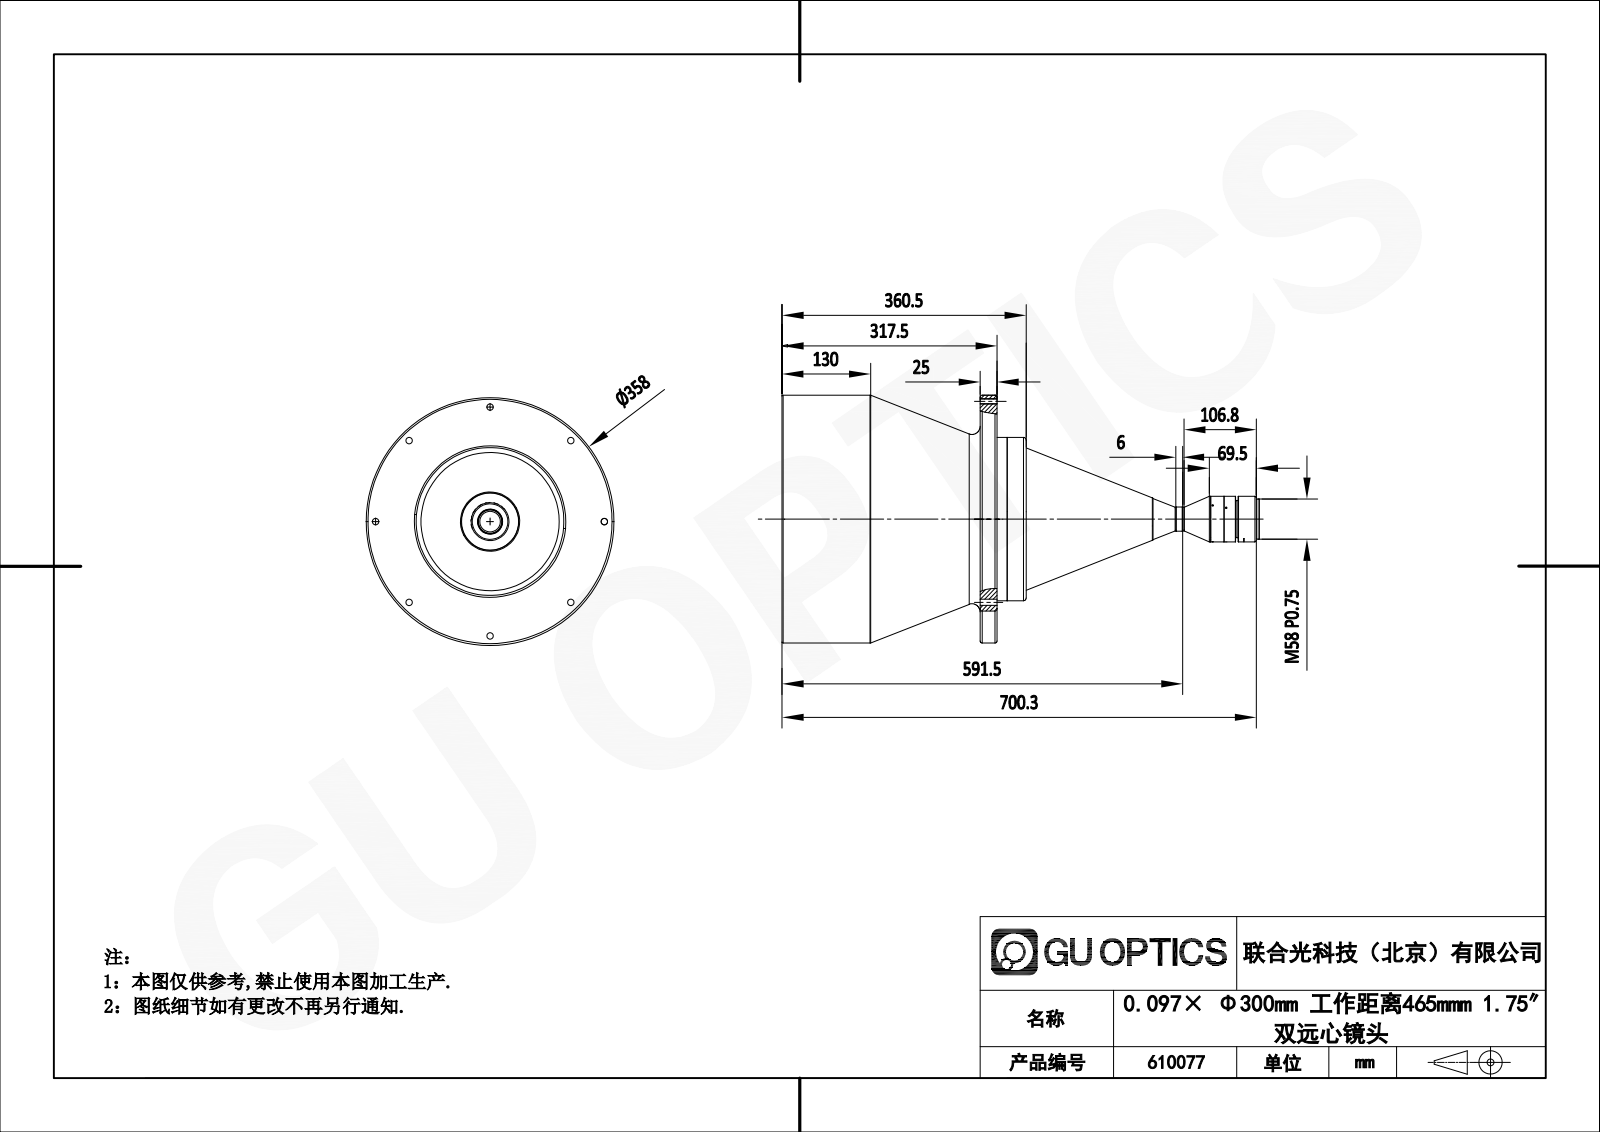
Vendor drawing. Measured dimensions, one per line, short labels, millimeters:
name: DTCM175-300S-M58-AL
written by: SolidWorks 2017 (CONFIG_CONTROL_DESIGN)
unit: mm
bodies: 1 solid, 159 faces (26 planar, 71 cylindrical, 62 other)
size: 704.76 × 358 × 358
volume: 31 790 000 mm³; area: 709 218 mm²
holes: 6× ⌀2.4, 4× ⌀6.8, 4× ⌀9, 1× ⌀32, 1× ⌀206, 1× ⌀340
bosses: 1× ⌀358, 1× ⌀236, 1× ⌀66, 1× ⌀58, 1× ⌀56.8, 1× ⌀35, 1× ⌀34, 1× ⌀31
rounds: 1× R1.25, 1× R1.75, 1× R3
face distances: 25, 68, 43, 292.5, 317.5, 360.5, 704.76, 412.26, 387.26, 344.26
hole spacings: 130.11, 170, 240.42, 314.12, 340, 340.01
